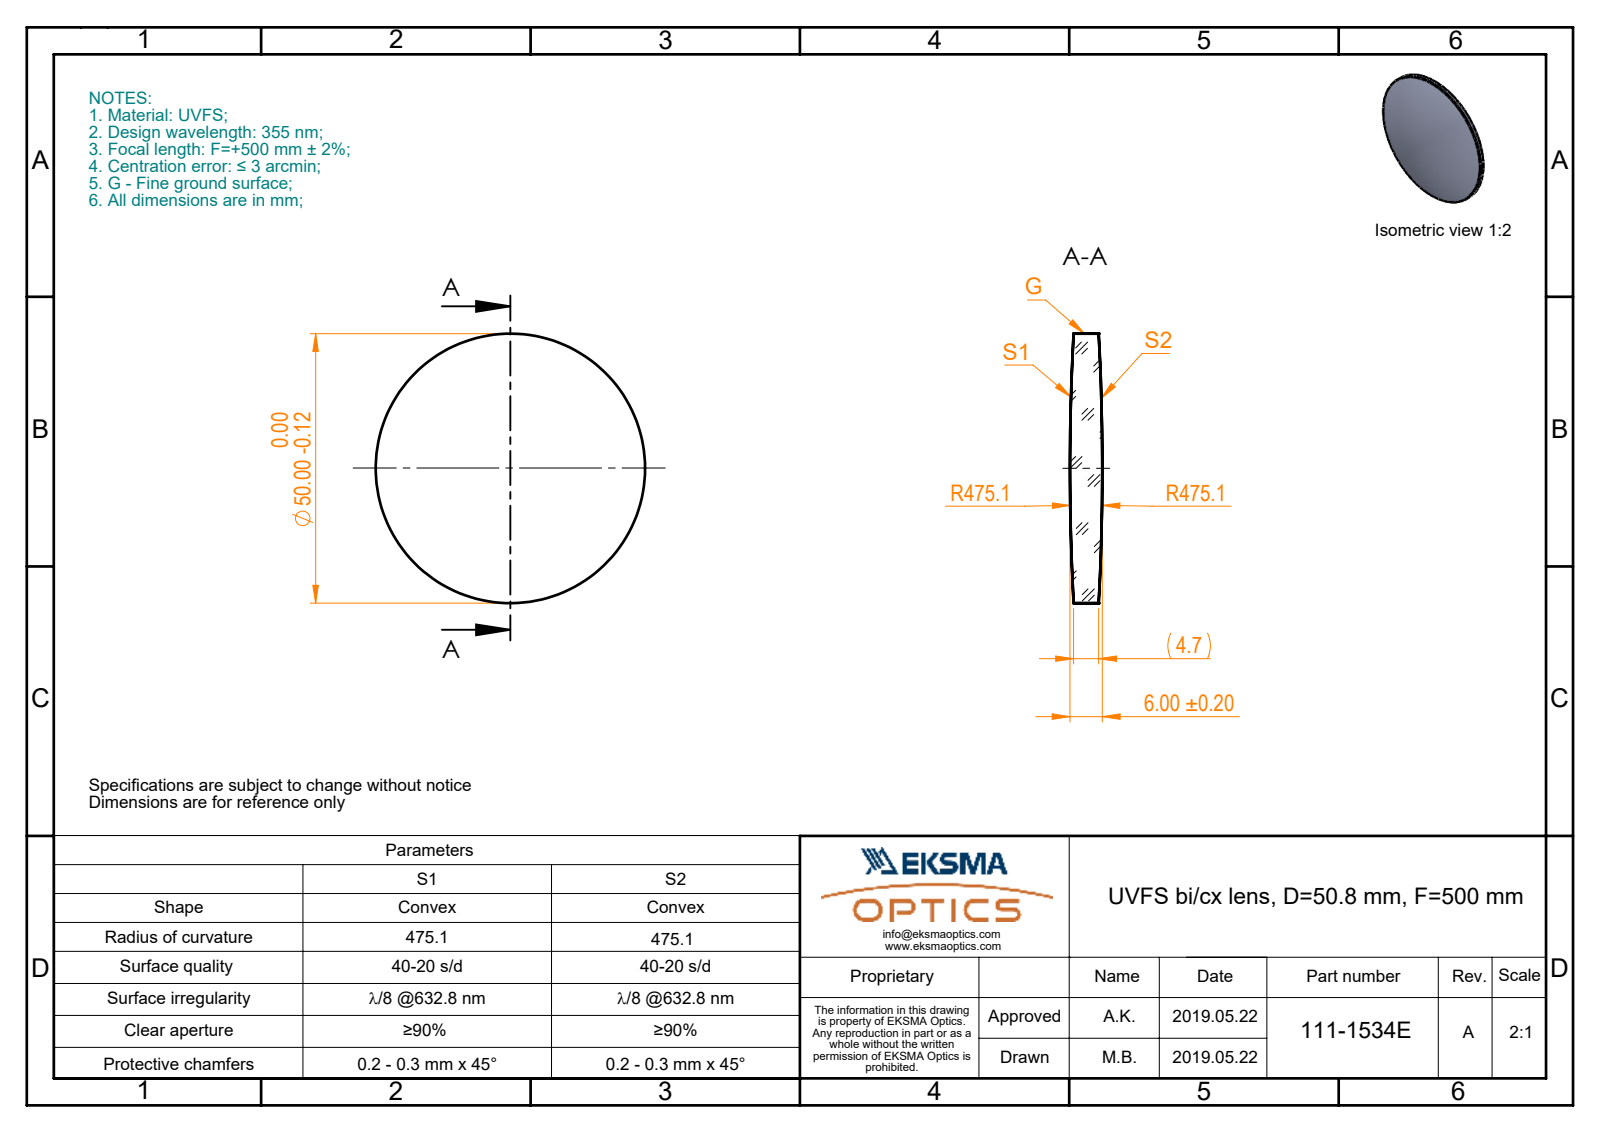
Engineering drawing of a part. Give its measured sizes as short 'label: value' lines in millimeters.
name: 111-1534E UVFS bi-cx 50.8 F500
written by: SolidWorks 2017 (CONFIG_CONTROL_DESIGN)
unit: mm
bodies: 1 solid, 6 faces (0 planar, 2 cylindrical, 4 other)
size: 50 × 50 × 6
volume: 10 489 mm³; area: 4 665 mm²
bosses: 1× ⌀50
